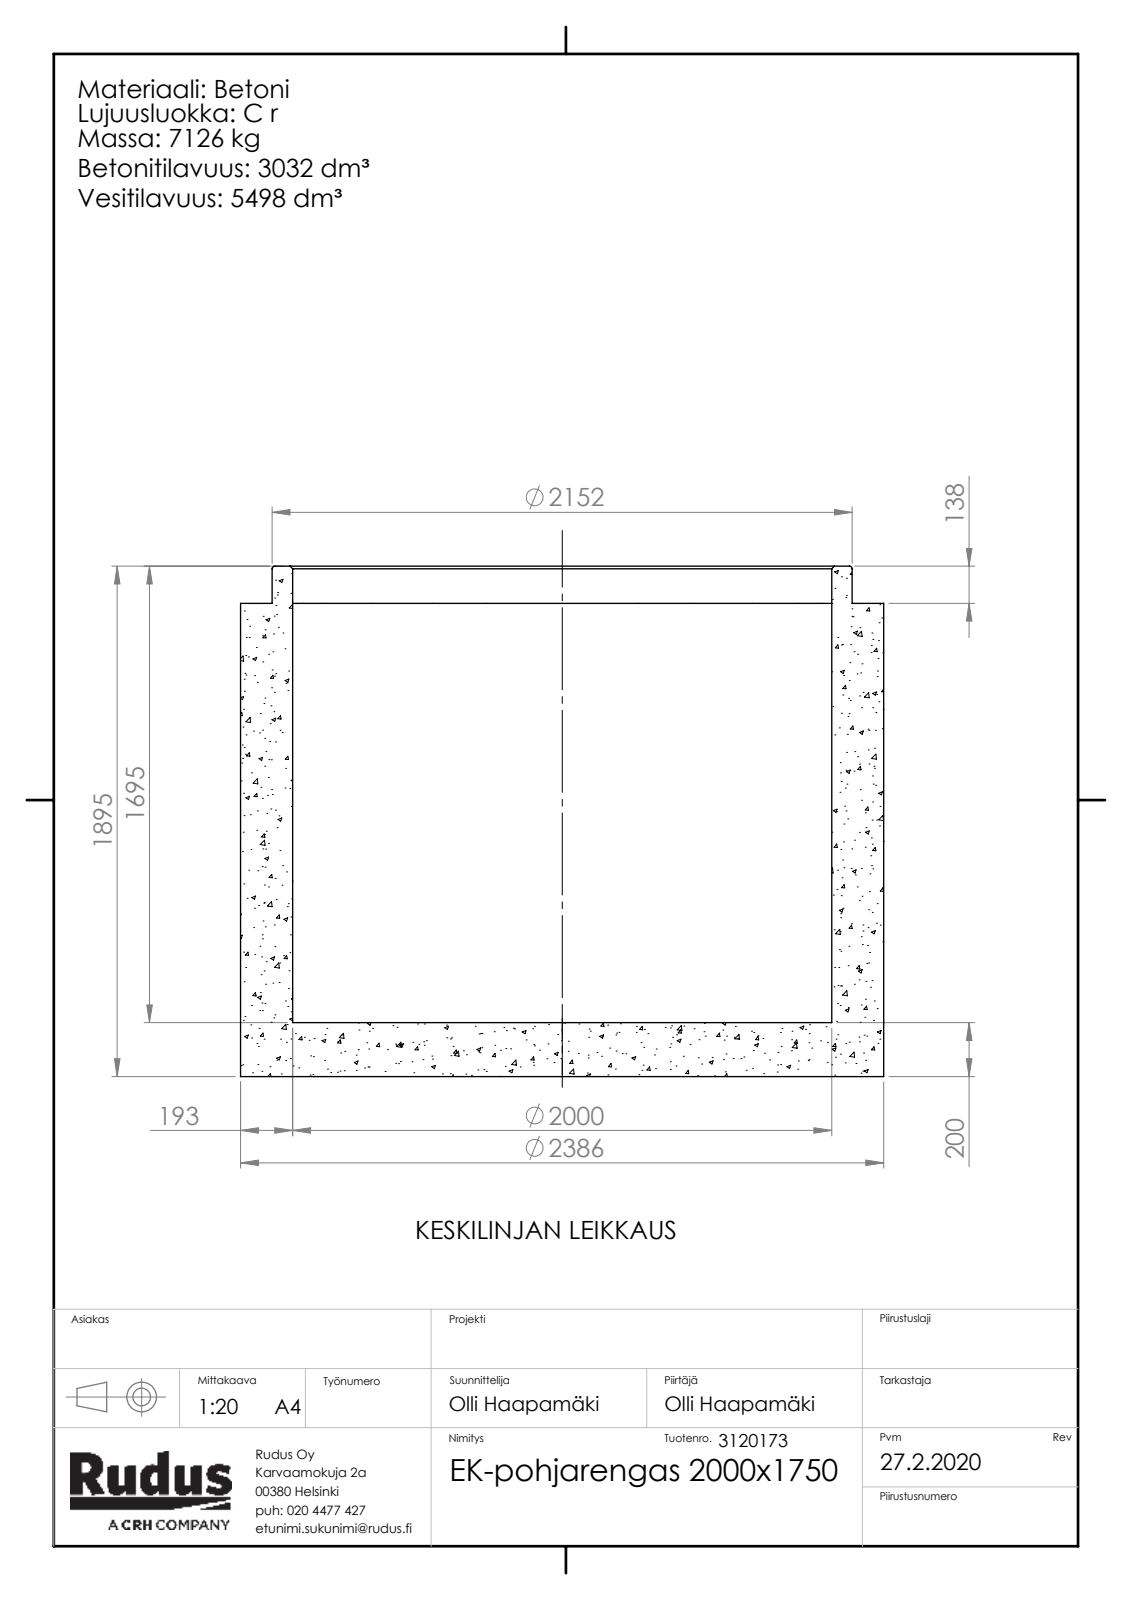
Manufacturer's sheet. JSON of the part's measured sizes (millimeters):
{"part_name": "EK-osa-kaivorunko_EK-pohjarengas; Rudus 3120173 EK-pohjarengas 2000x1750", "step_written_by": "SolidWorks 2019 (CONFIG_CONTROL_DESIGN)", "units": "millimeters", "bodies": {"solids": 1, "faces": 95, "planar": 5, "cylindrical": 6, "other": 84}, "overall_size": [2386, 2386, 1895], "volume_mm3": 3033000000, "surface_area_mm2": 33630000, "round_holes": [[2000, 1]], "round_bosses_or_shafts": [[2386, 1], [2152, 1]], "face_to_face_distances": [200, 1757, 1557, 1895, 1695, 138, 1060.55, 860.55, 696.45, 834.45]}
